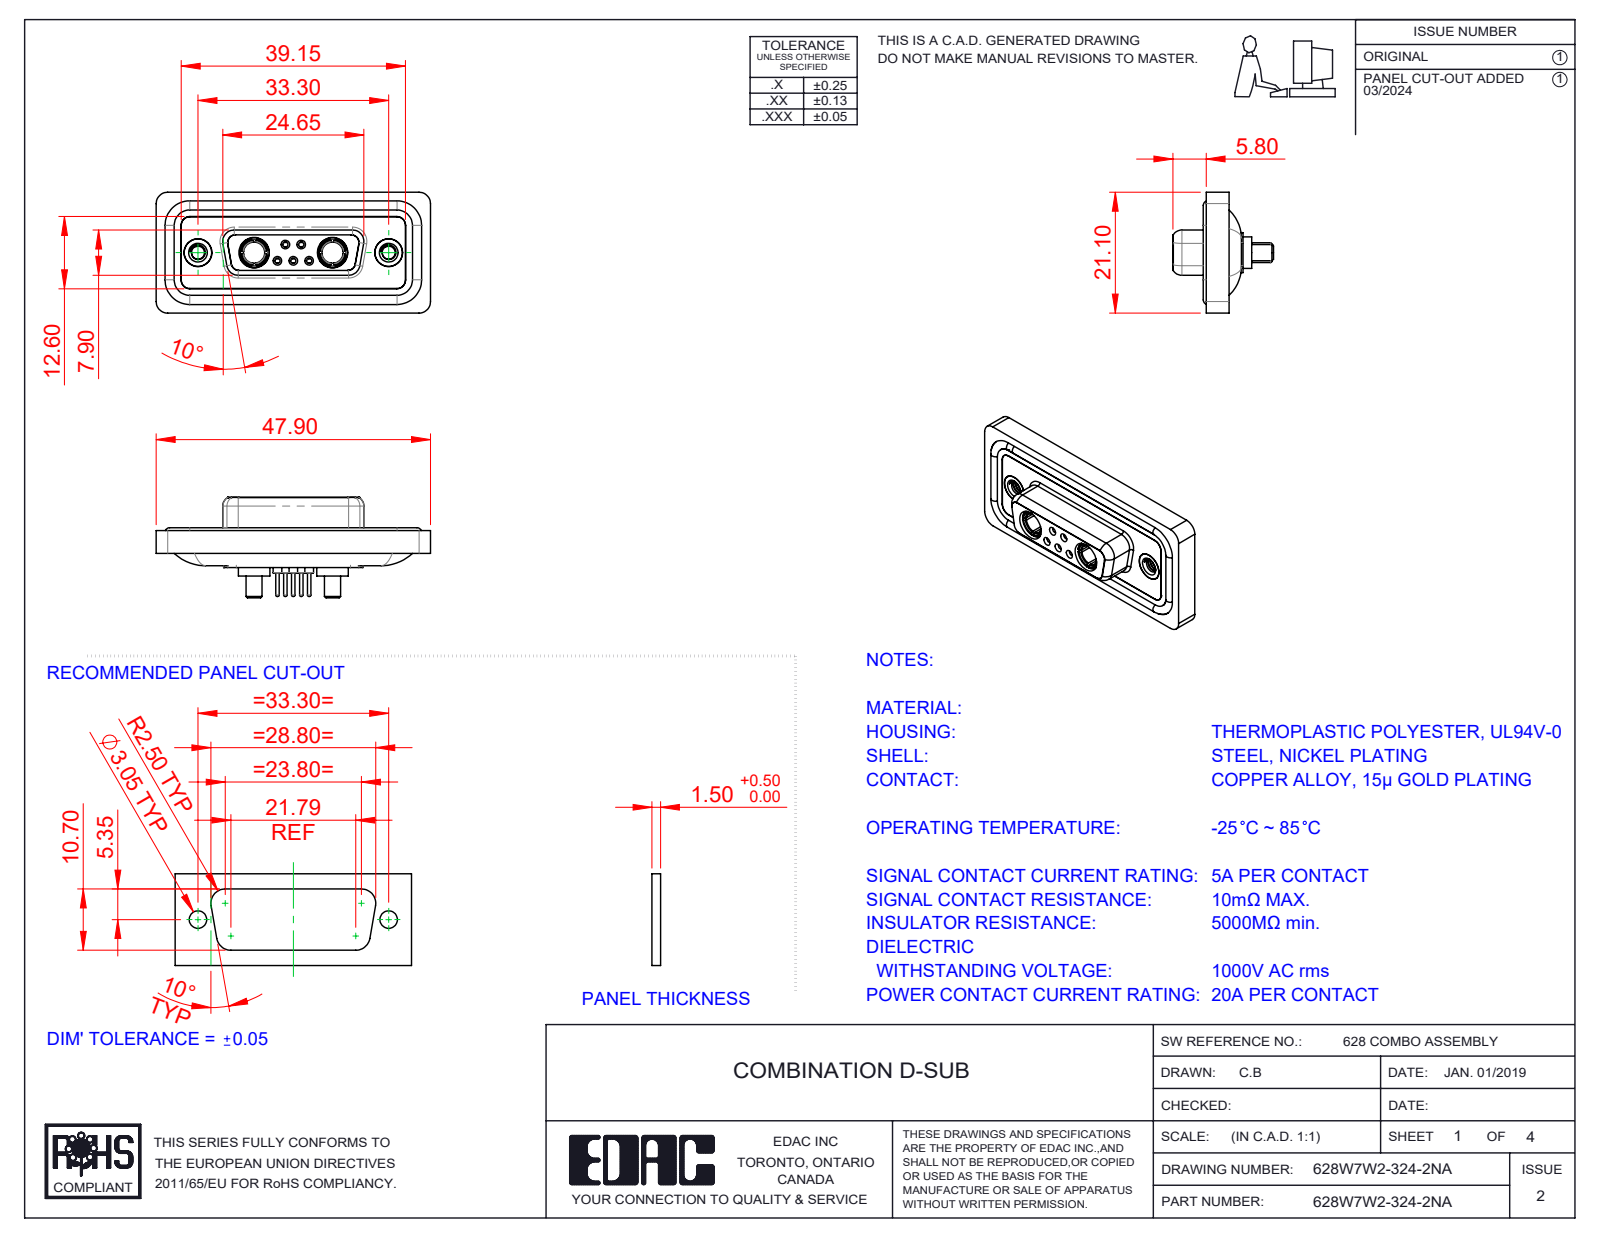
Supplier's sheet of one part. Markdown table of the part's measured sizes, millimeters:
| quantity | value |
| --- | --- |
| part name | 628Combo Contact Row 1_24; 628Combo Threaded Rivet_A; 628Combo Contact Row 2_24; 628Combo Housing_7W2 (+5 more) |
| STEP written by | SolidWorks 2023 (CONFIG_CONTROL_DESIGN) |
| units | millimeters |
| bodies | 16 solids, 807 faces (238 planar, 331 cylindrical, 238 other) |
| overall size | 47.9 × 21.1 × 17.55 |
| volume | 6 079 mm³ |
| surface area | 9 883 mm² |
| round holes (diameter × count) | 0.9 × 5, 1.1 × 5, 1.5 × 5, 2 × 5, 4.85 × 4, 1.6 × 3, 1.7 × 2, 2.26 × 2, 3.7 × 2, 4 × 2, 4.05 × 2, 5 × 2 |
| round bosses / shafts (diameter × count) | 1.6 × 6, 2.2 × 5, 0.6 × 5, 5.5 × 2, 5.2 × 2, 4.96 × 2, 4.95 × 2, 4.8 × 2 |
| partial cylindrical surfaces (radius × count) | 1.5 × 22, 2 × 20, 1.35 × 12, 1.6 × 8, 0.25 × 4, 0.5 × 4, 0.6 × 4, 0.65 × 4 |
| main face-to-face distances | 0.4, 1.8, 1.6, 0.5, 2.9, 7.45, 1.1, 5.65, 6.6, 7.05 |
| hole center spacings | 3.16, 2.77, 9.8, 23.5, 4.31, 4.33, 5.03, 5.04 |
